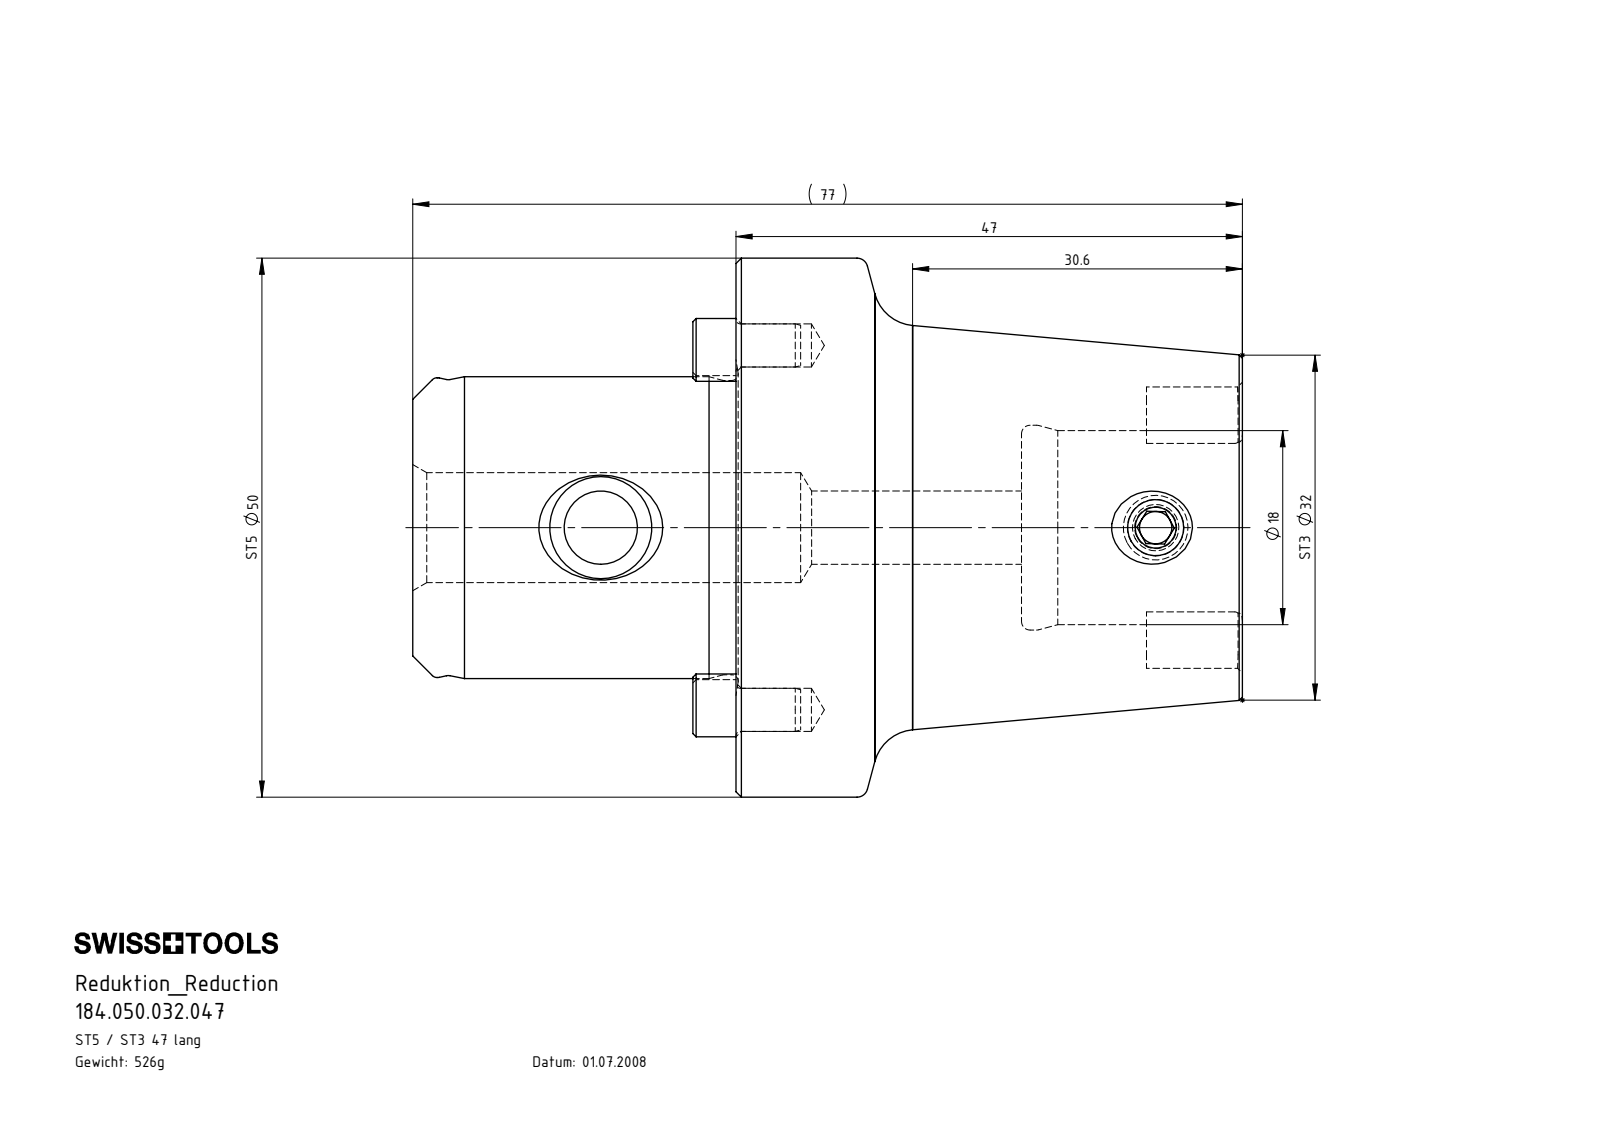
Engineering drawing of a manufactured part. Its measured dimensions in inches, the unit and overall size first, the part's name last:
Units: inches
Overall size (bounding box): 3.031 × 1.969 × 1.969
Round holes (diameter × count): ⌀0.157 ×2, ⌀0.268 ×2, ⌀0.207 ×1, ⌀0.402 ×1, ⌀0.709 ×1, ⌀0.748 ×1
Round bosses / shafts (diameter × count): ⌀1.969 ×1, ⌀1.102 ×1, ⌀1.094 ×1, ⌀1.075 ×1, ⌀0.236 ×1
Partial cylindrical surfaces — rounded edges, fillets, slot ends (radius × count): R0.02 ×4, R0.098 ×2, R0.176 ×2, R0.553 ×2
Main face-to-face distances: 1.85, 1.181, 3.031, 0.807, 2.224, 1.043, 0.612, 1.024, 0.157, 1.201
Hole centre spacings: 0.665, 1.331, 2.028
Volume: 4.087 in³ · Surface area: 23.87 in²
Bodies: 4 solids, 162 faces (26 planar, 45 cylindrical, 91 other)
Part name (STEP PRODUCT): ST5-ST3.K01.047_A; ST5-ST3.K01.047; ST5-ER2.001.010_A; ST3-ER1.001.008_A
STEP written by: SolidWorks 2015 (CONFIG_CONTROL_DESIGN)
